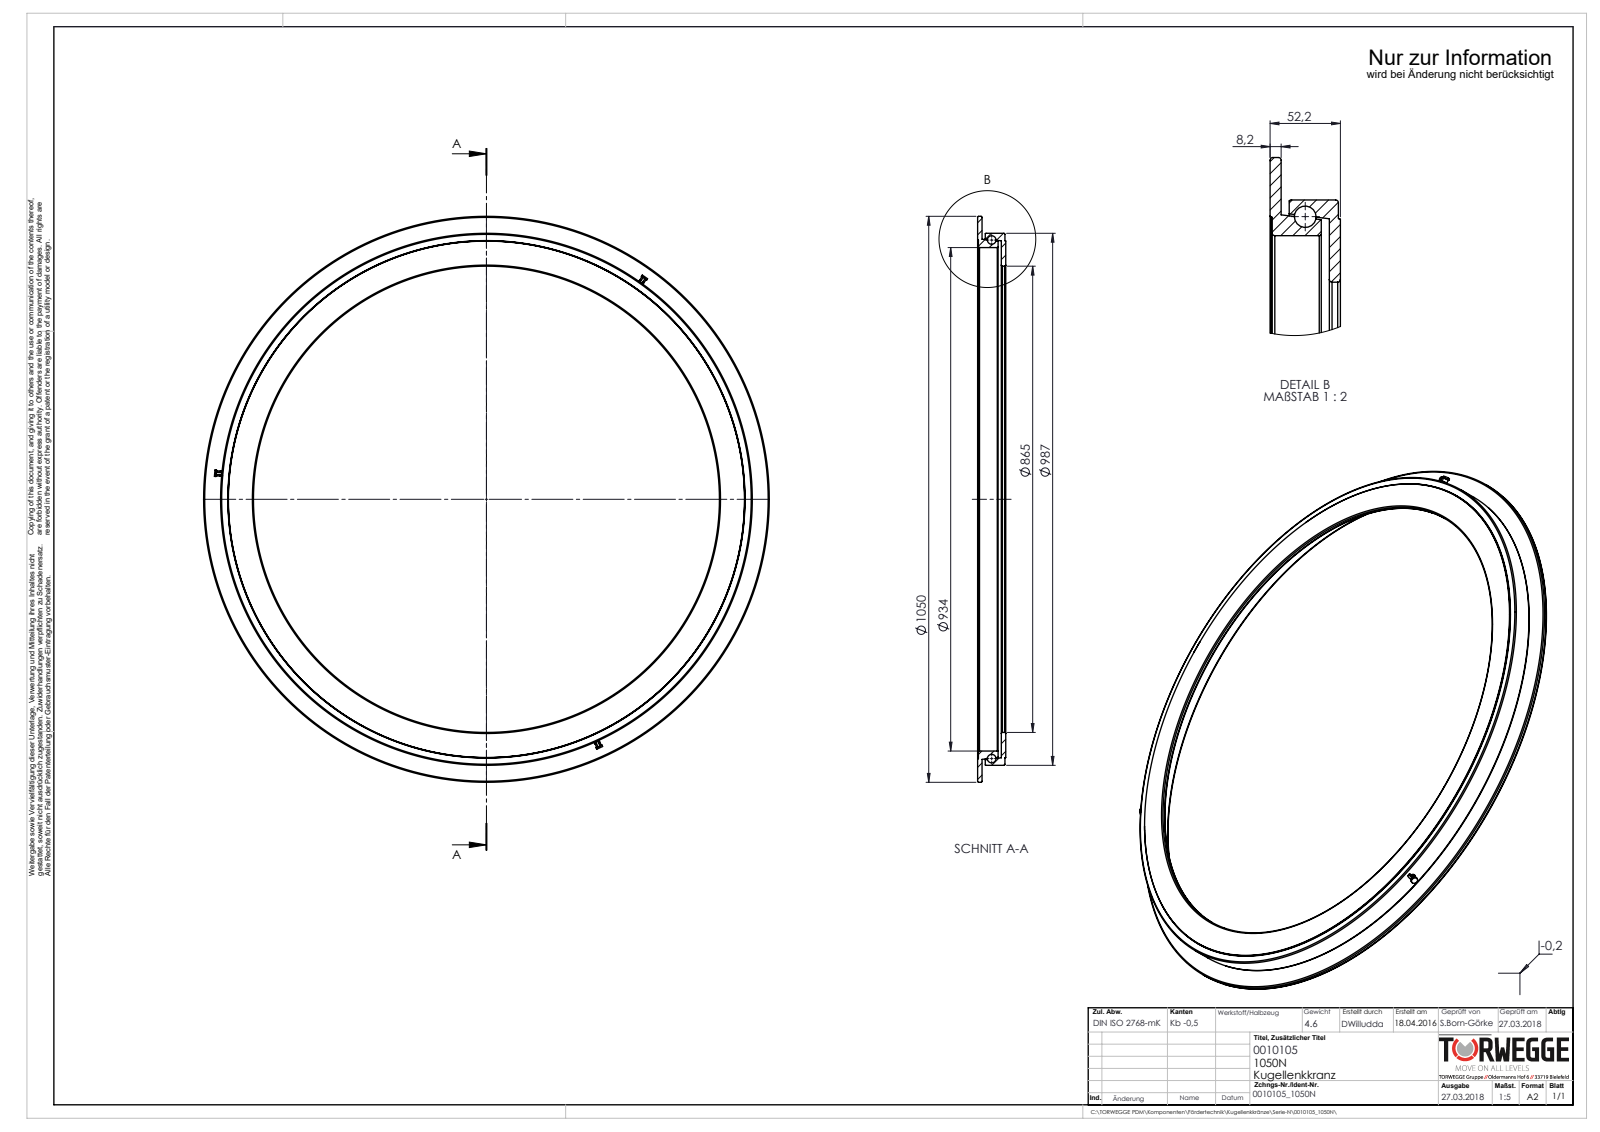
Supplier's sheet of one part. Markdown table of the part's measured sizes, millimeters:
| quantity | value |
| --- | --- |
| part name | 1050N_Teil1; 1050N_Teil2; 0010105_1050N; JS-1101-021 (+1 more) |
| STEP written by | SolidWorks 2018 (AUTOMOTIVE_DESIGN) |
| units | millimeters |
| bodies | 8 solids, 263 faces (65 planar, 64 cylindrical, 134 other) |
| overall size | 1050 × 1050 × 52.2 |
| volume | 4 576 000 mm³ |
| surface area | 1 184 000 mm² |
| round holes (diameter × count) | 6 × 5, 1.5 × 3, 864.96 × 1, 934 × 1 |
| round bosses / shafts (diameter × count) | 12 × 3, 7.5 × 3, 1050 × 1, 987 × 1, 958.99 × 1 |
| partial cylindrical surfaces (radius × count) | 1.75 × 3, 4.62 × 3, 5 × 3, 5.62 × 3 |
| main face-to-face distances | 44, 52.2, 8.2, 1.5, 50.7, 6.7, 42.5, 49.2, 38.01, 36.51 |
